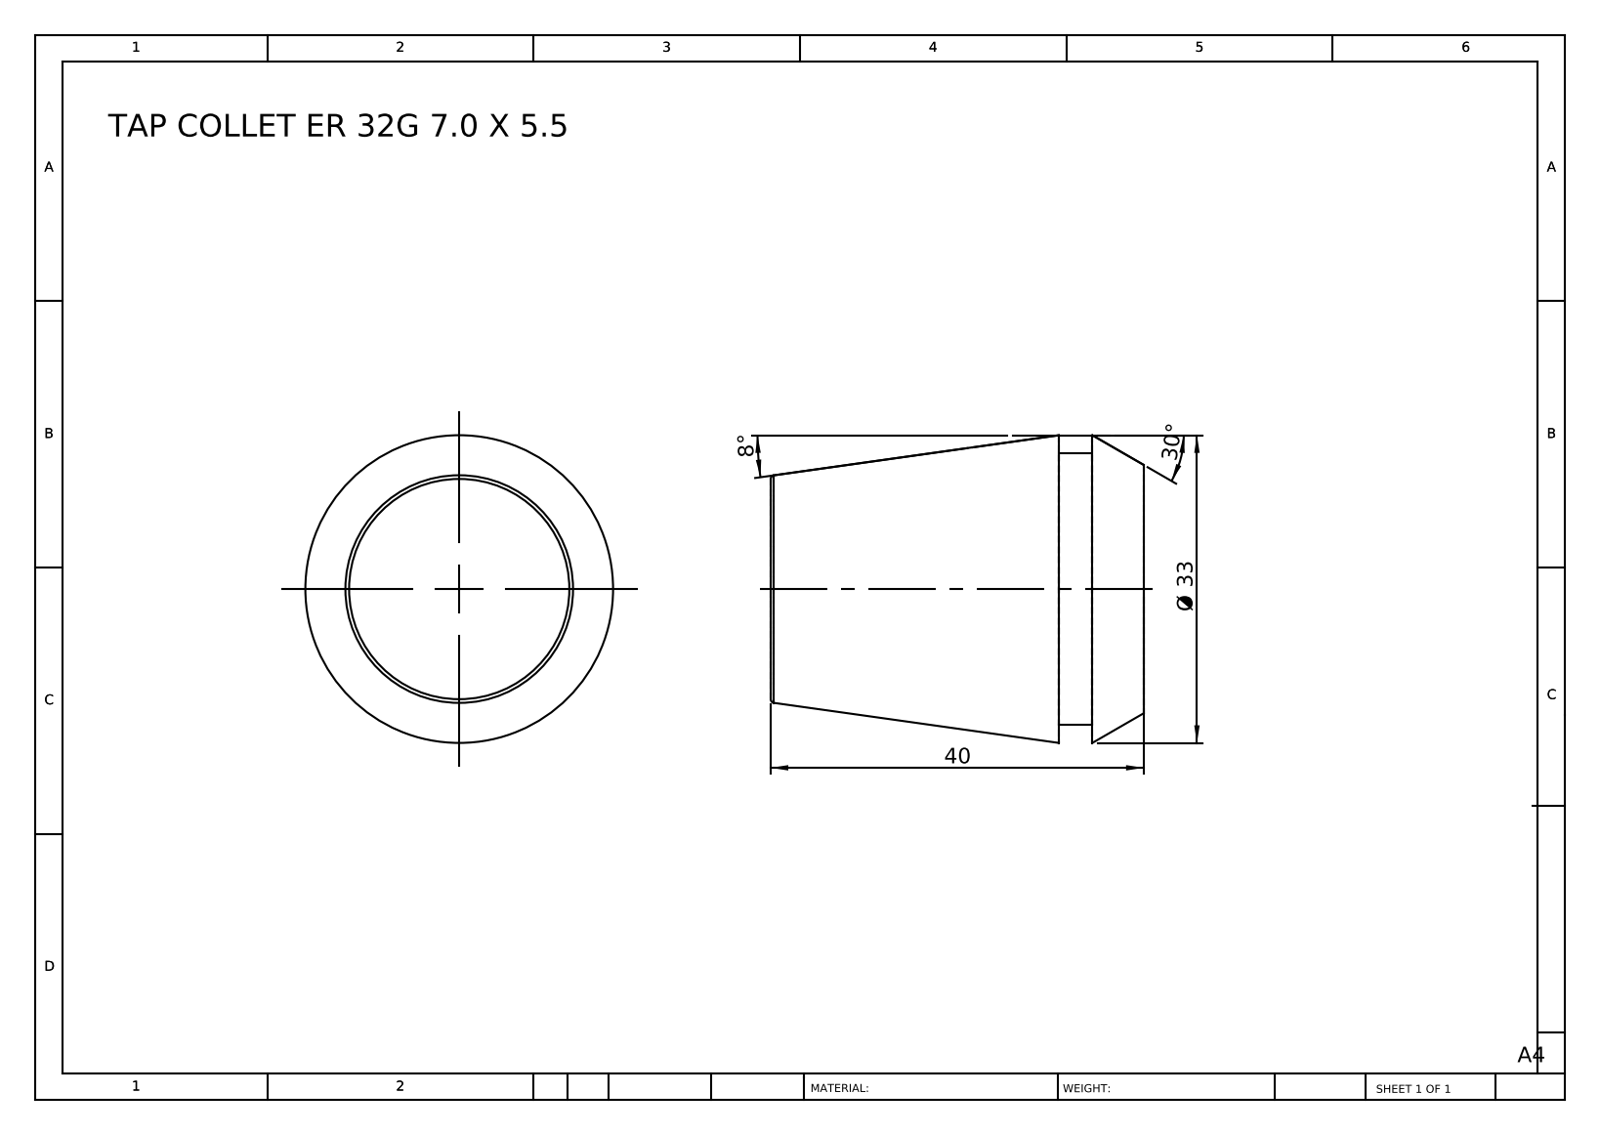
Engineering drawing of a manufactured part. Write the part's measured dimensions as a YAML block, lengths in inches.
part_name: "TAP COLLET ER 32G 7.0 X 5.5"
step_written_by: "SolidWorks 2014 (CONFIG_CONTROL_DESIGN)"
units: inches
bodies: {solids: 1, faces: 12, planar: 4, cylindrical: 2, other: 6}
overall_size: [1.575, 1.299, 1.299]
volume: 1.608
surface_area: 7.934
round_bosses_or_shafts:
  - {diameter: 1.15, count: 1}
face_to_face_distances: [1.575, 0.358, 1.217, 0.217, 0.142, 1.358]
